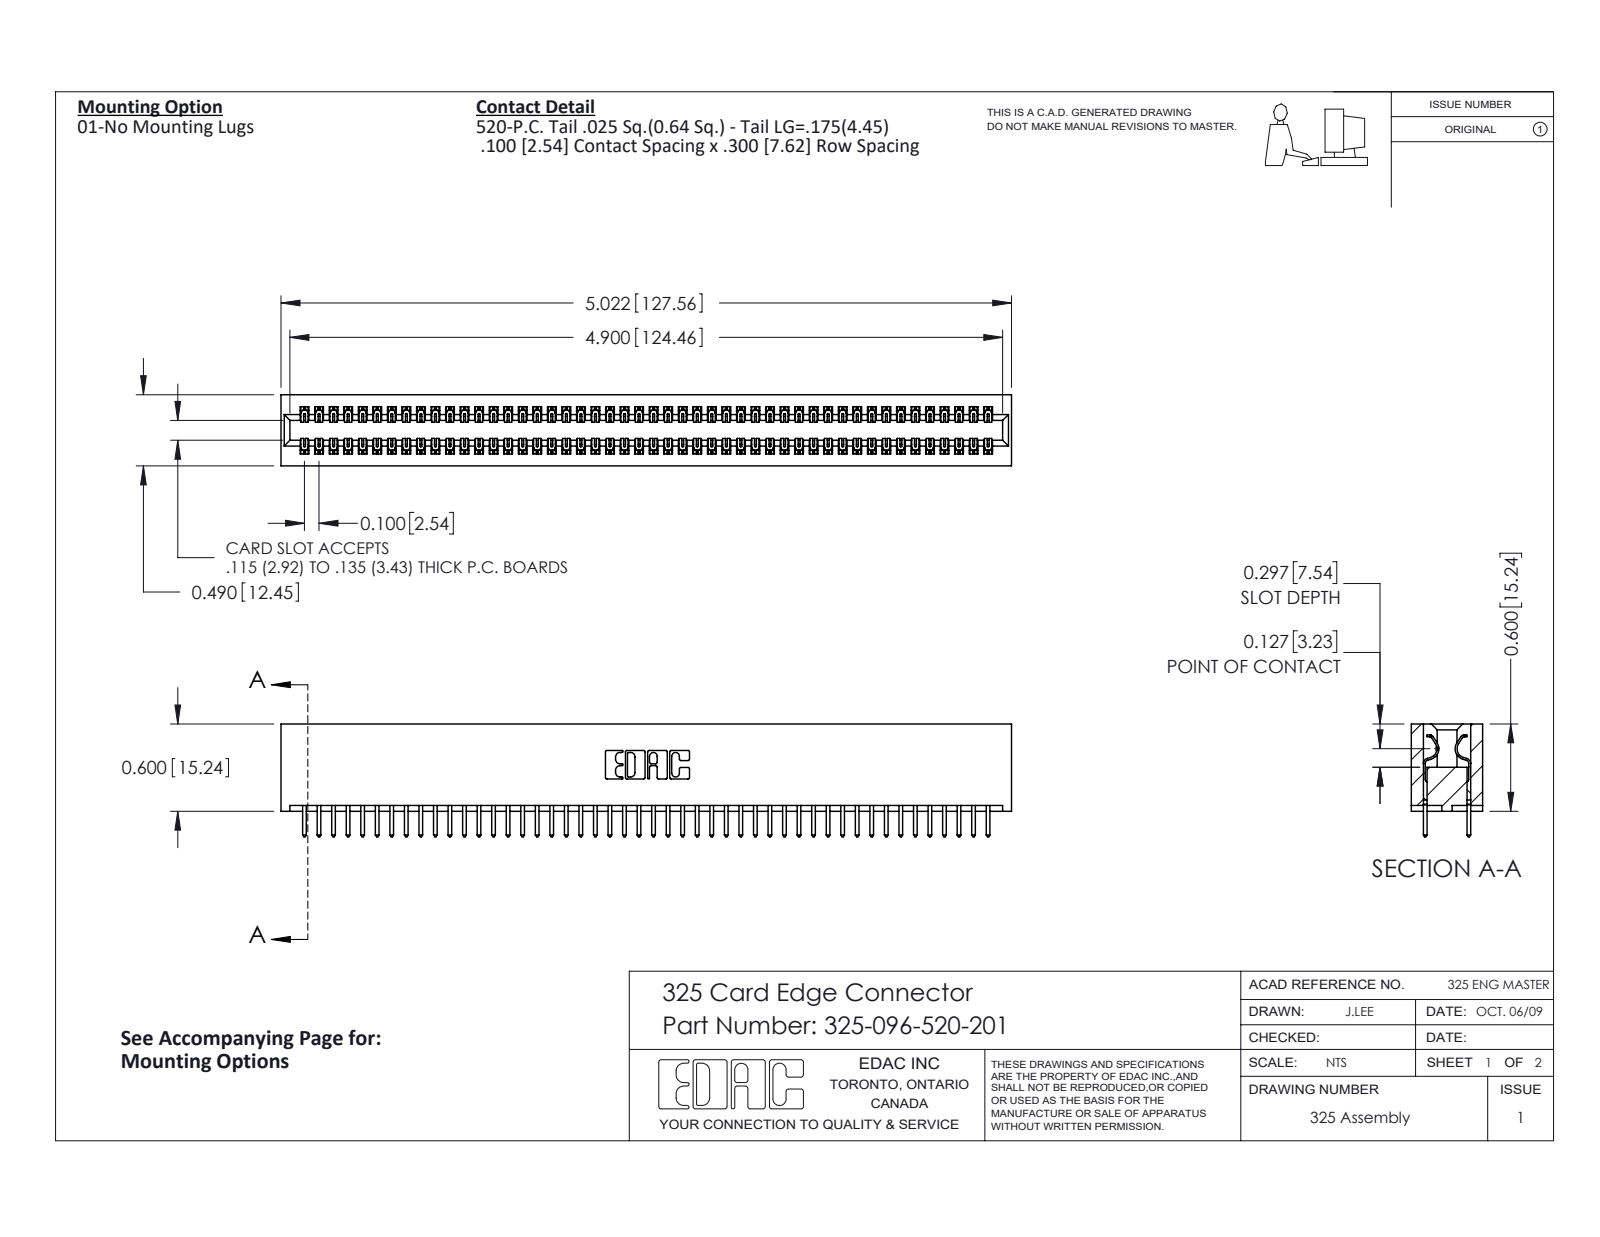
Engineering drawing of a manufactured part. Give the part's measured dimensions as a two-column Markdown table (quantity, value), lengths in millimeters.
| quantity | value |
| --- | --- |
| part name | 325-096-520-201; 325 Part_Lugless; 325-292-001_325-293-120 |
| STEP written by | SolidWorks 2016 (CONFIG_CONTROL_DESIGN) |
| units | millimeters |
| bodies | 97 solids, 5098 faces (3522 planar, 1576 cylindrical, 0 other) |
| overall size | 127.6 × 19.7 × 12.4 |
| volume | 17 110 mm³ |
| surface area | 21 320 mm² |
| partial cylindrical surfaces (radius × count) | 0.2 × 144, 0.3 × 96, 0.3 × 22, 0.2 × 6, 0.8 × 6, 0.7 × 3, 0.4 × 2, 0.6 × 2 |
| main face-to-face distances | 2.1, 10.3, 7.6, 12.4, 2.7, 9.7, 0.6, 8.3, 7, 14.2 |
